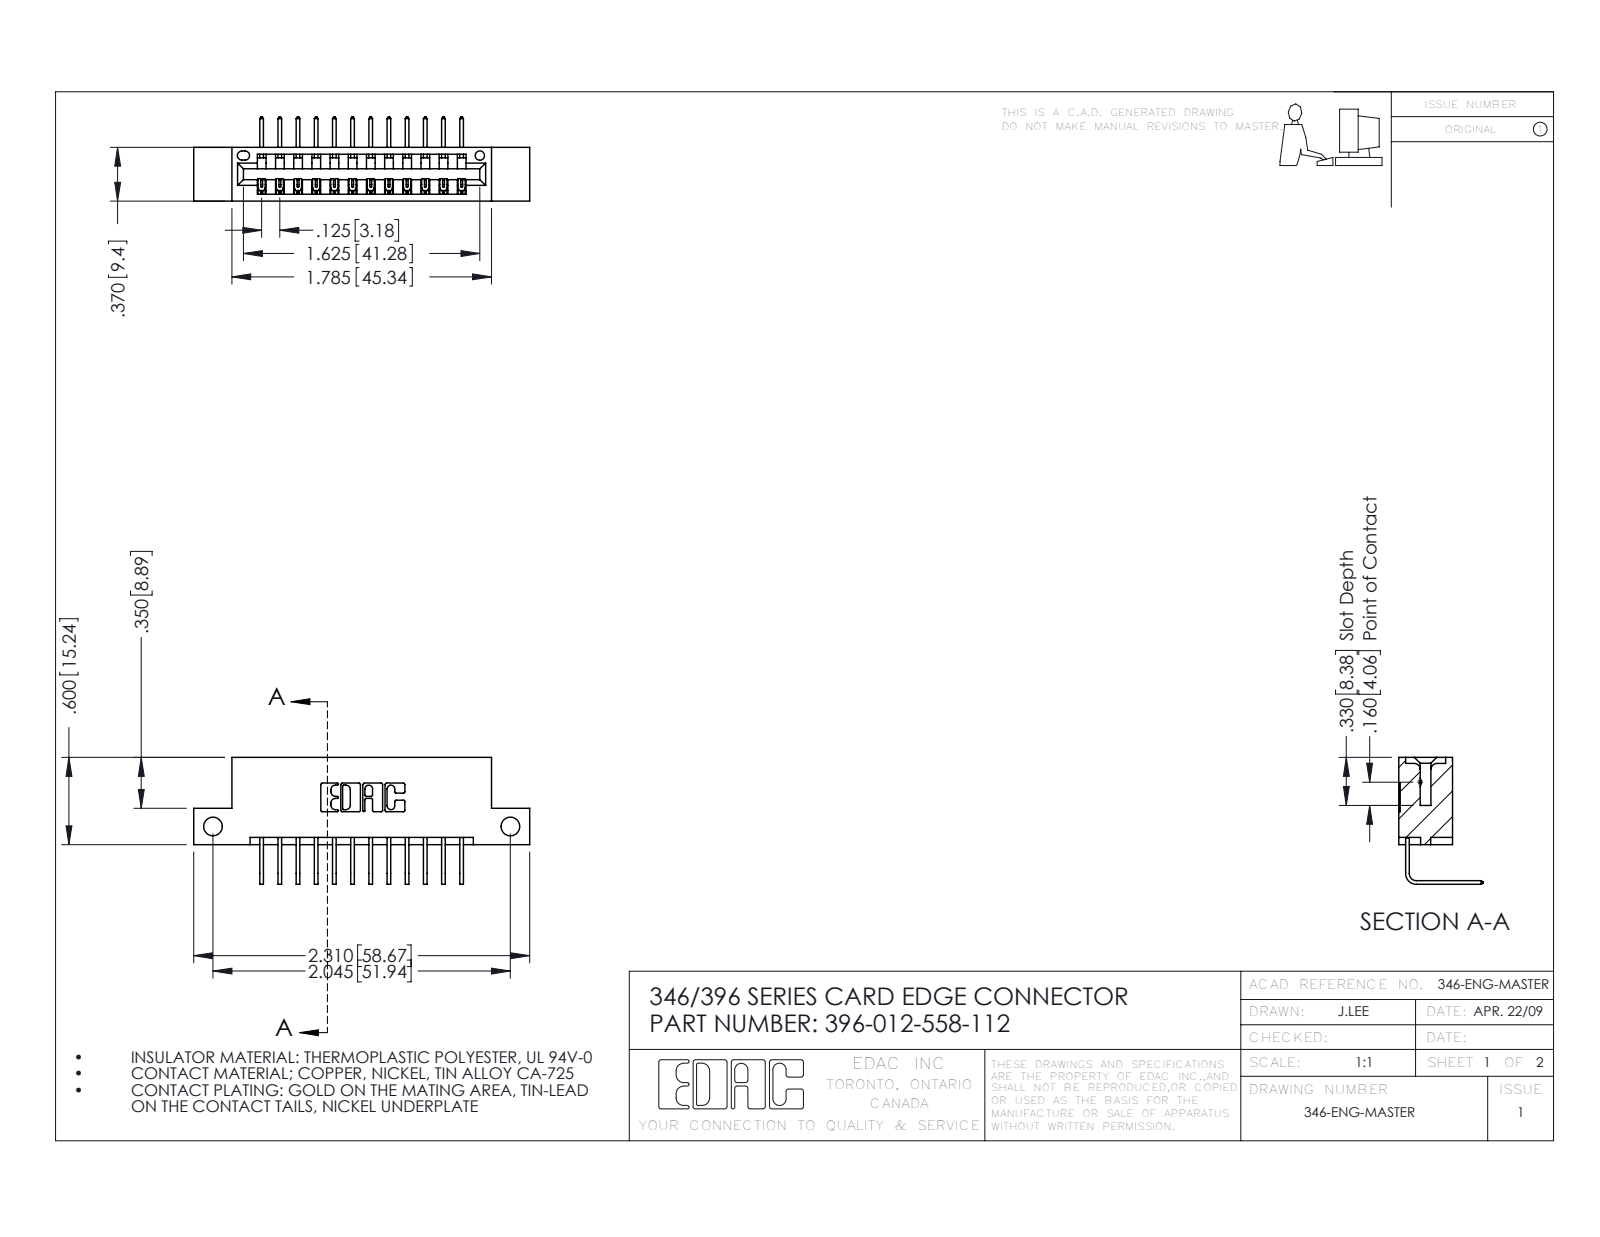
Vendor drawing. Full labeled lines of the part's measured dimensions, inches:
Part name (STEP PRODUCT): 396-012-558-112; 345-292-001_558 Tail - 2; 346 Part_Flush Mounting Lugs - Side Mount
STEP written by: SolidWorks 2016 (CONFIG_CONTROL_DESIGN)
Units: inches
Bodies: 13 solids, 842 faces (580 planar, 262 cylindrical, 0 other)
Overall size (bounding box): 2.31 × 0.873 × 0.58
Volume: 0.327 in³ · Surface area: 10.03 in²
Round holes (diameter × count): ⌀0.128 ×2, ⌀0.064 ×1
Partial cylindrical surfaces — rounded edges, fillets, slot ends (radius × count): R0.006 ×24, R0.01 ×22, R0.007 ×6, R0.031 ×6, R0.026 ×3, R0.031 ×2, R0.04 ×2, R0.014 ×1
Main face-to-face distances: 0.25, 0.322, 0.048, 0.37, 0.298, 0.025, 0.072, 0.148, 0.222, 0.1
Hole centre spacings: 2.045
